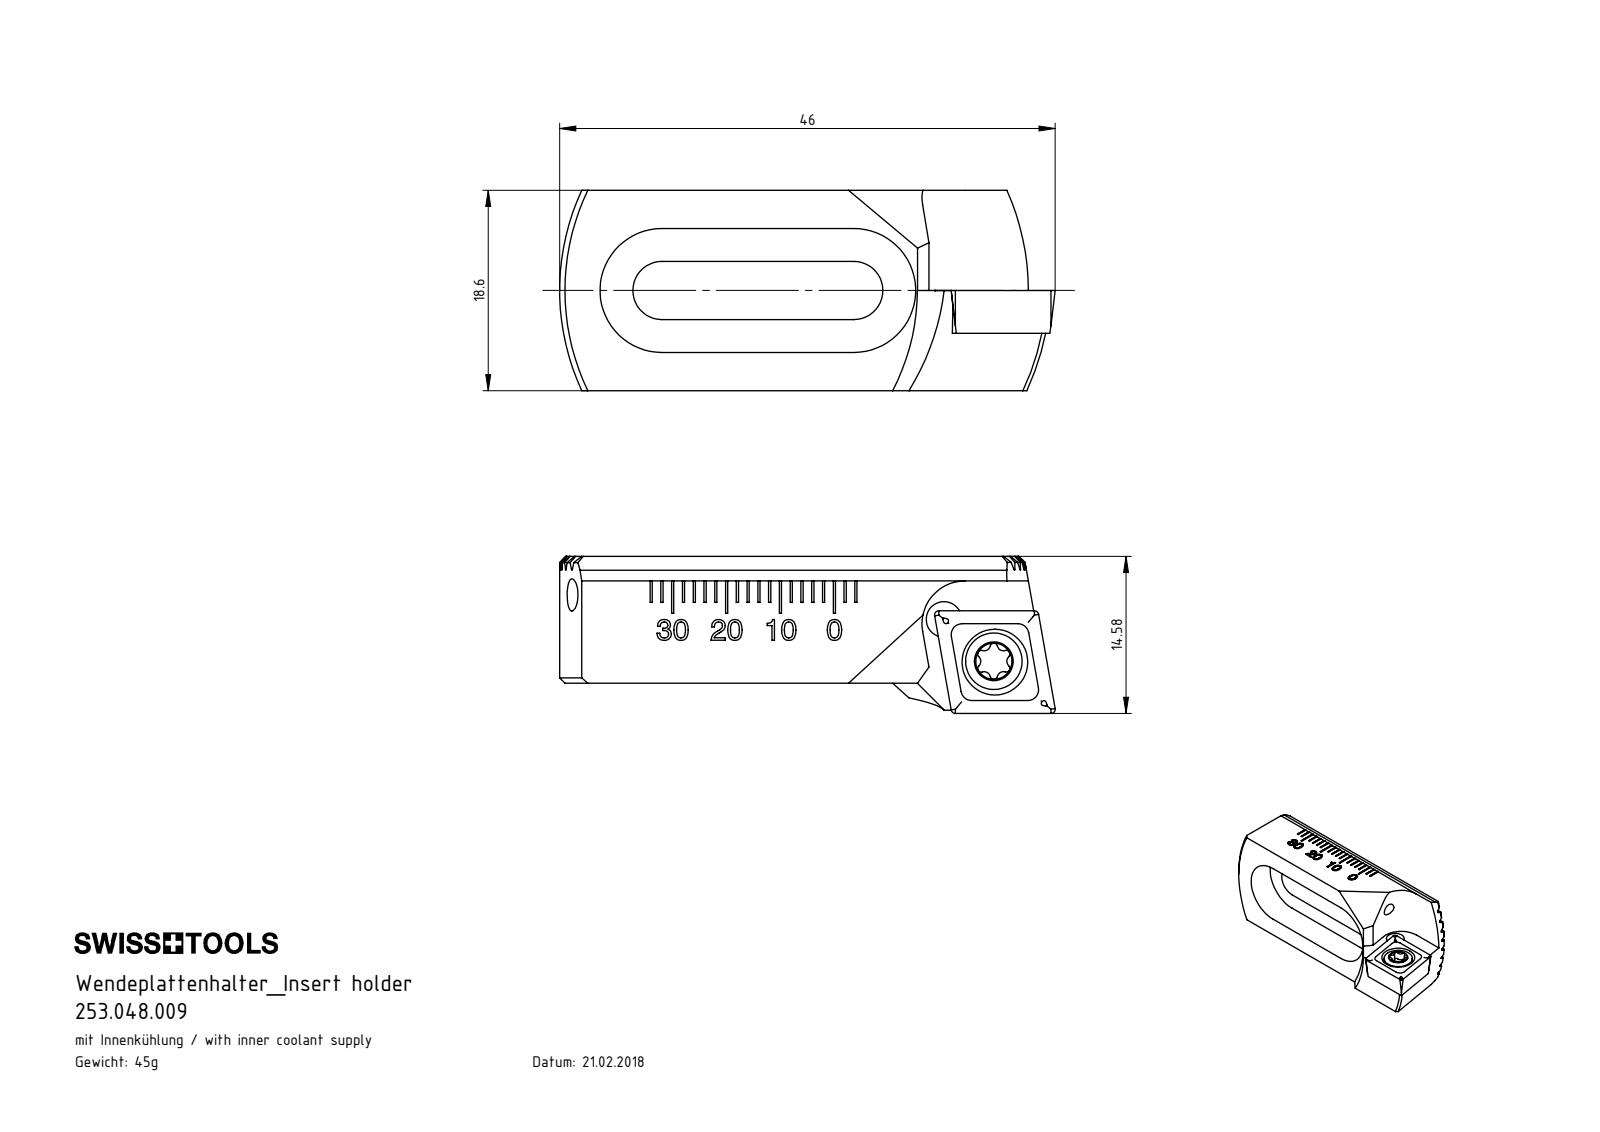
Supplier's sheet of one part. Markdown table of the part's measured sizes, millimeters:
| quantity | value |
| --- | --- |
| part name | BV2-WCB.K11.014_B; CCMT09T304; 253.048.009; KVT_MB_600_030 (+1 more) |
| STEP written by | SolidWorks 2017 (CONFIG_CONTROL_DESIGN) |
| units | millimeters |
| bodies | 5 solids, 444 faces (210 planar, 77 cylindrical, 157 other) |
| overall size | 46 × 18.6 × 14.58 |
| volume | 5 758 mm³ |
| surface area | 4 615 mm² |
| round holes (diameter × count) | 2 × 3, 3.3 × 2, 2.38 × 1, 4.4 × 1, 6.1 × 1 |
| round bosses / shafts (diameter × count) | 5.25 × 1, 4 × 1, 3 × 1 |
| partial cylindrical surfaces (radius × count) | 0.14 × 10, 0.34 × 6, 0.59 × 6, 2.7 × 2, 5.75 × 2, 4 × 1, 22 × 1, 23 × 1 |
| main face-to-face distances | 1.73, 3.46, 8.66, 10.39, 6.93, 18.6, 12.12, 12, 6.6, 5.2 |
| hole center spacings | 6.35, 6.47 |
